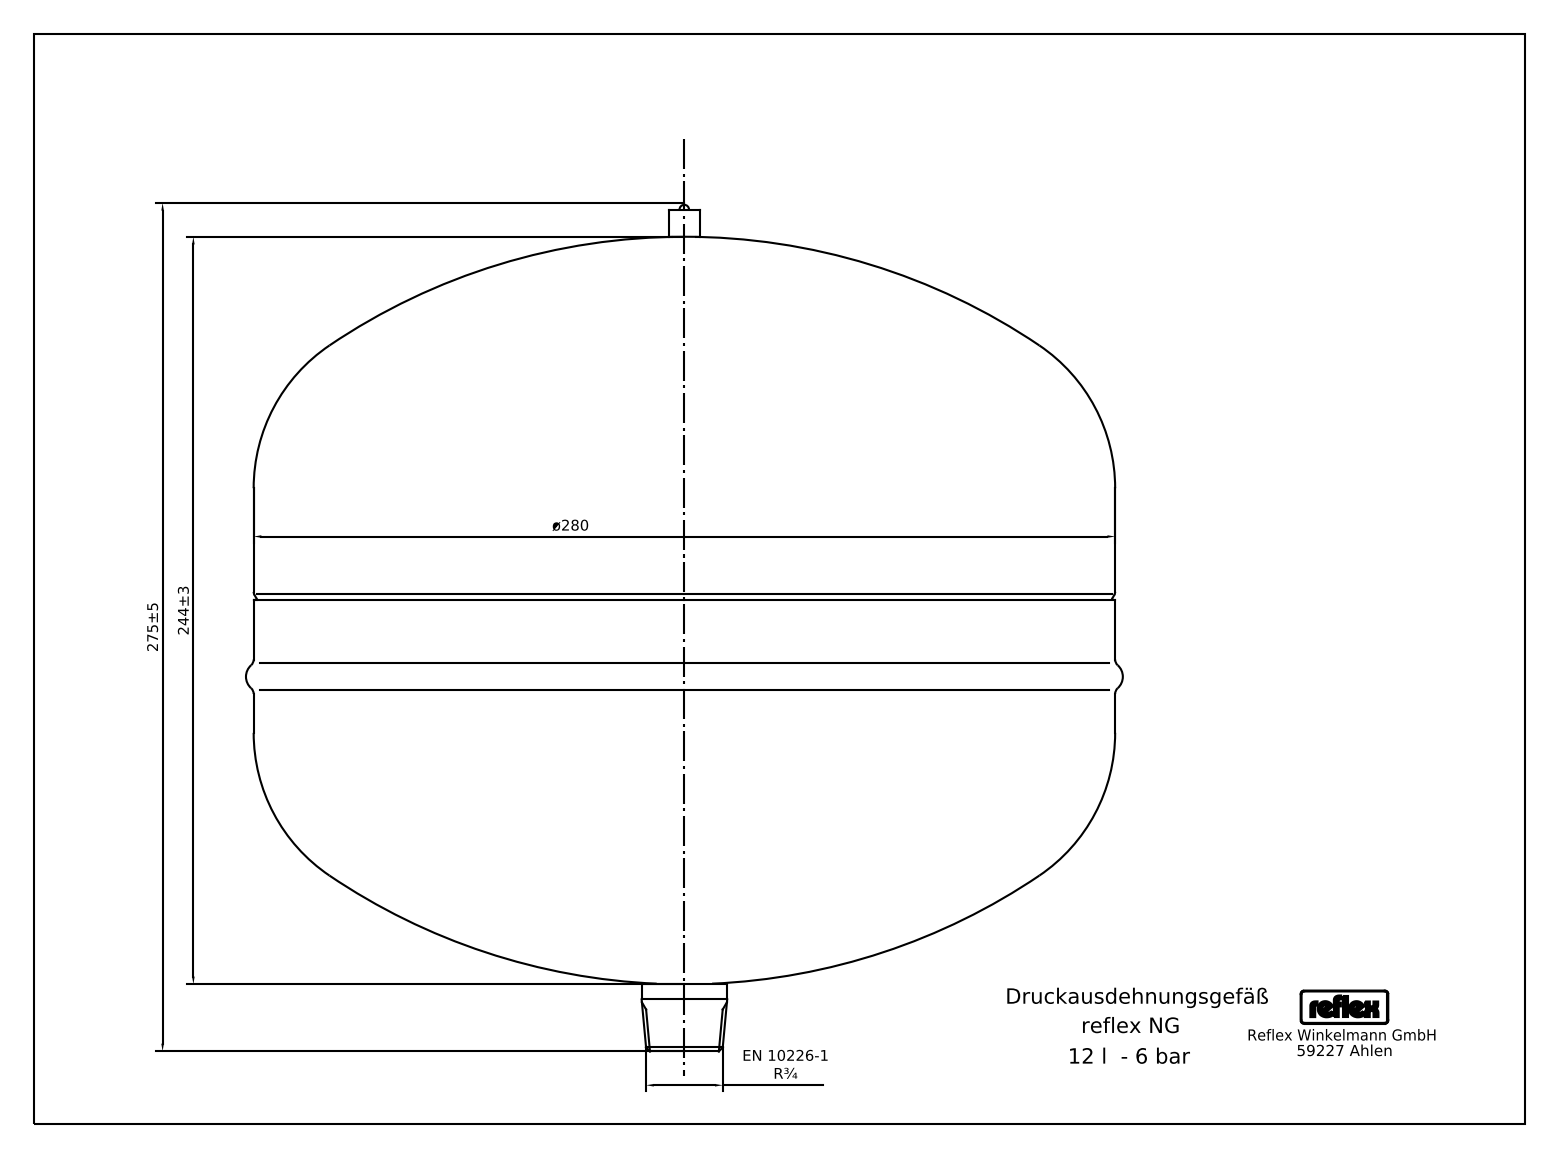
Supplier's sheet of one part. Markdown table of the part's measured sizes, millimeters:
| quantity | value |
| --- | --- |
| STEP written by | Mechanical Desktop 2011 (CONFIG_CONTROL_DESIGN) |
| units | millimeters |
| bodies | 13 solids, 125 faces (64 planar, 38 cylindrical, 23 other) |
| overall size | 302 × 302 × 275 |
| volume | 12 590 000 mm³ |
| surface area | 565 446 mm² |
| round holes (diameter × count) | 18.9 × 1 |
| round bosses / shafts (diameter × count) | 302 × 1, 280 × 1, 26.9 × 1, 10 × 1, 6 × 1 |
| partial cylindrical surfaces (radius × count) | 1.12 × 4, 0.45 × 3, 0.77 × 2, 1.35 × 2, 1.85 × 2, 1.88 × 2, 2.54 × 2, 0.56 × 1 |
| main face-to-face distances | 131, 57.5, 73.5, 16, 20, 75, 132.5, 148.5, 206, 55 |
